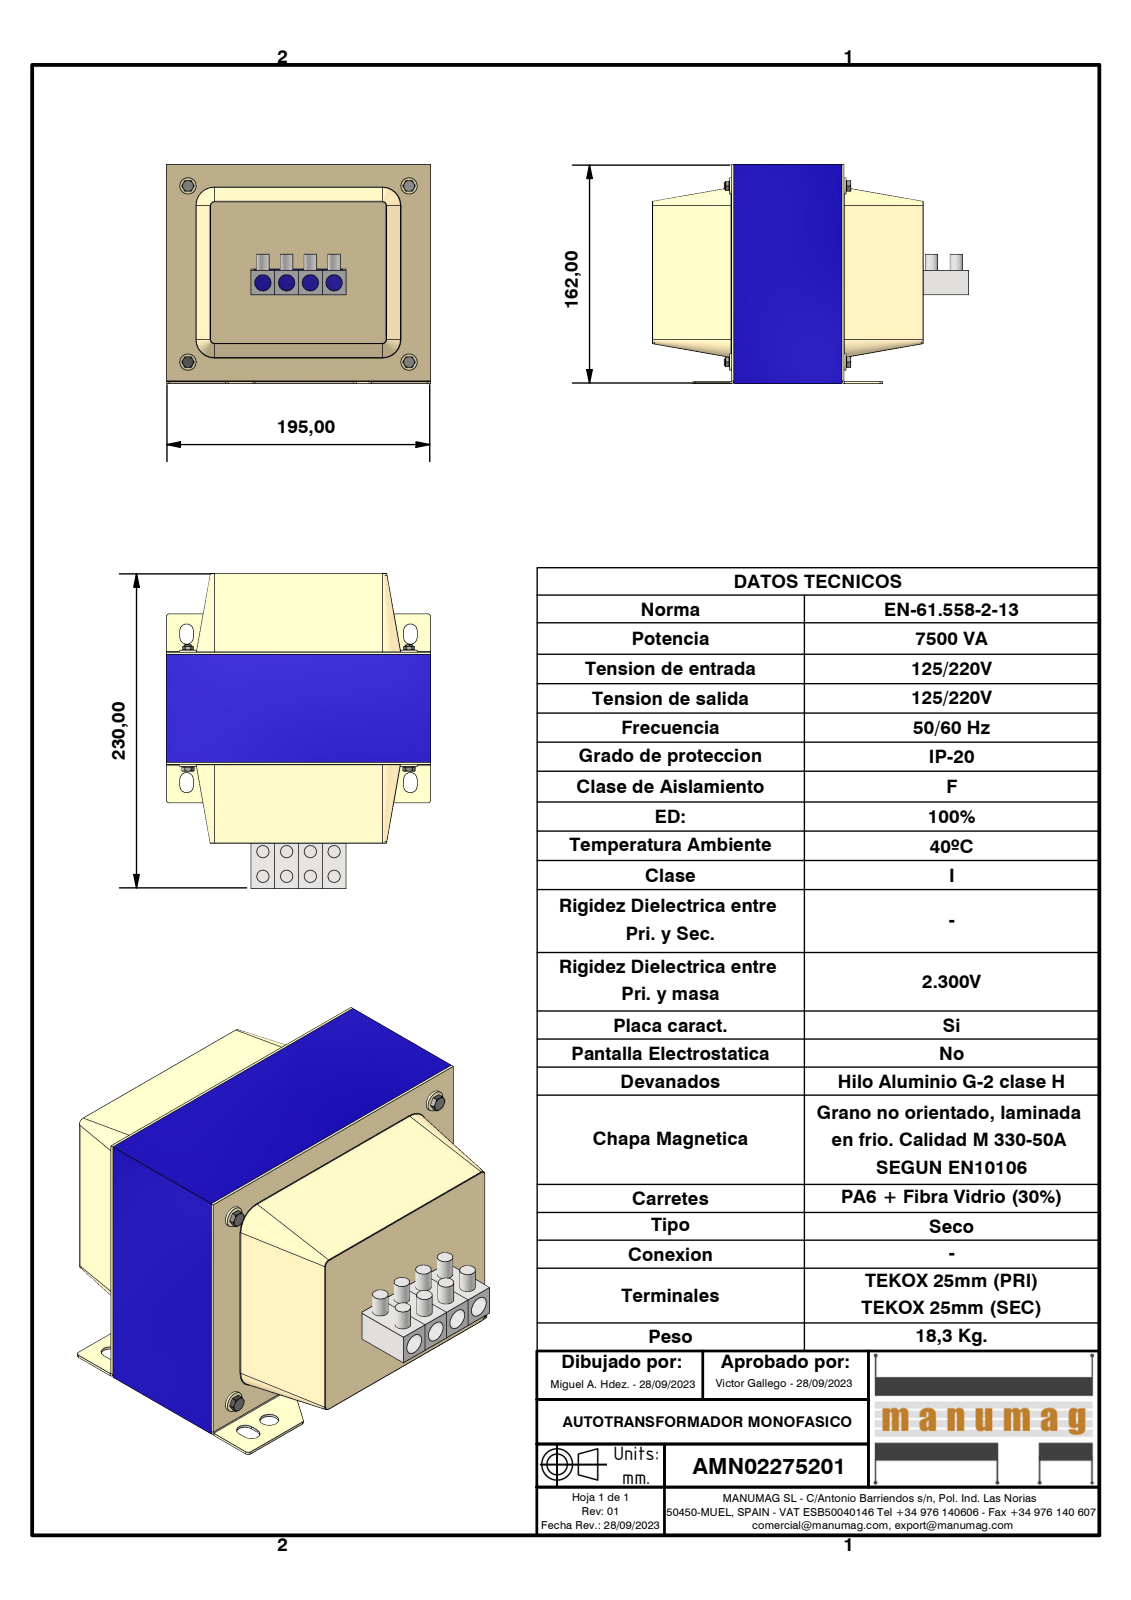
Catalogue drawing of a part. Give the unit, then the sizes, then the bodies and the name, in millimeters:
Units: millimetres
Overall size (bounding box): 233.5 × 195 × 162
Round holes (diameter × count): ⌀11 ×8, ⌀3.24 ×4, ⌀5 ×4, ⌀9 ×4, ⌀12 ×4
Round bosses / shafts (diameter × count): ⌀9 ×8, ⌀12 ×4, ⌀6.7 ×4, ⌀5.9 ×4, ⌀4.57 ×4
Partial cylindrical surfaces — rounded edges, fillets, slot ends (radius × count): R0.38 ×16, R2 ×14, R5 ×8, R0.5 ×2
Main face-to-face distances: 1.5, 58.5, 140, 80, 130, 32.5, 138.5, 65, 60, 57
Hole centre spacings: 17.5, 35, 80.47, 90.36, 93.35, 102, 107.55, 110
Volume: 2 131 000 mm³ · Surface area: 423 584 mm²
Bodies: 23 solids, 402 faces (202 planar, 112 cylindrical, 88 other)
Part name (STEP PRODUCT): AMN02275201; EI195 x 162 - 80 (Rc65) Azul; TAPA RC65 CIEGA; TAPA RC65 VENTANA 4 ELEMENTOS 25 (+5 more)
STEP written by: Autodesk Inventor 2023 (AUTOMOTIVE_DESIGN)
